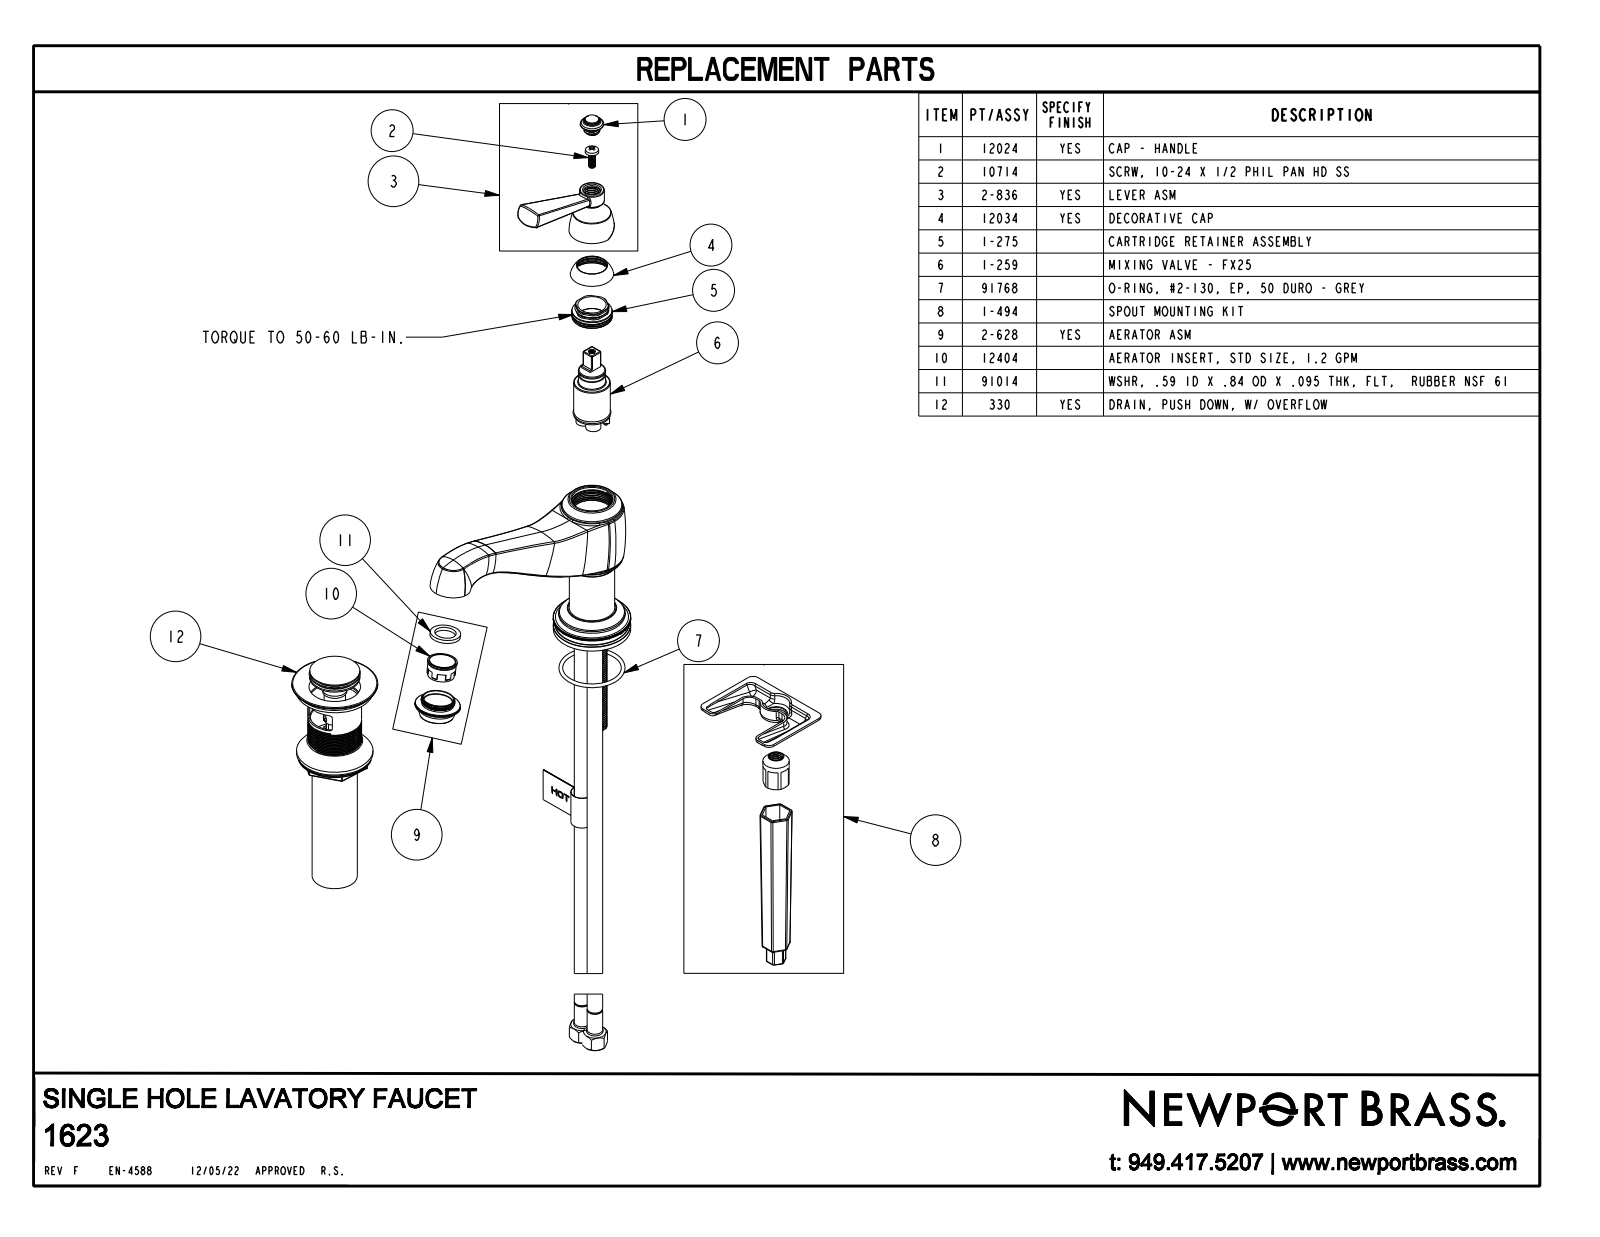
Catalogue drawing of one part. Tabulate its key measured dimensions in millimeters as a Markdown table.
| quantity | value |
| --- | --- |
| part name | 1623_SW0001 |
| STEP written by | CREO PARAMETRIC BY PTC INC, 2018400 (AUTOMOTIVE_DESIGN) |
| units | millimeters |
| bodies | 2 solids, 1107 faces (579 planar, 303 cylindrical, 225 other) |
| overall size | 182.9 × 162.4 × 54.1 |
| volume | 267 900 mm³ |
| surface area | 41 540 mm² |
| round holes (diameter × count) | 4.5 × 1, 28.6 × 1 |
| round bosses / shafts (diameter × count) | 54.1 × 1, 51.8 × 1, 46.5 × 1, 42.7 × 1, 31.8 × 1, 25.4 × 1, 17.3 × 1, 16.4 × 1 |
| partial cylindrical surfaces (radius × count) | 15.9 × 1 |
| main face-to-face distances | 108.7, 111.3, 2.5, 7.4, 10.2, 98.6, 101.1, 8.5, 1.6, 100.2 |
